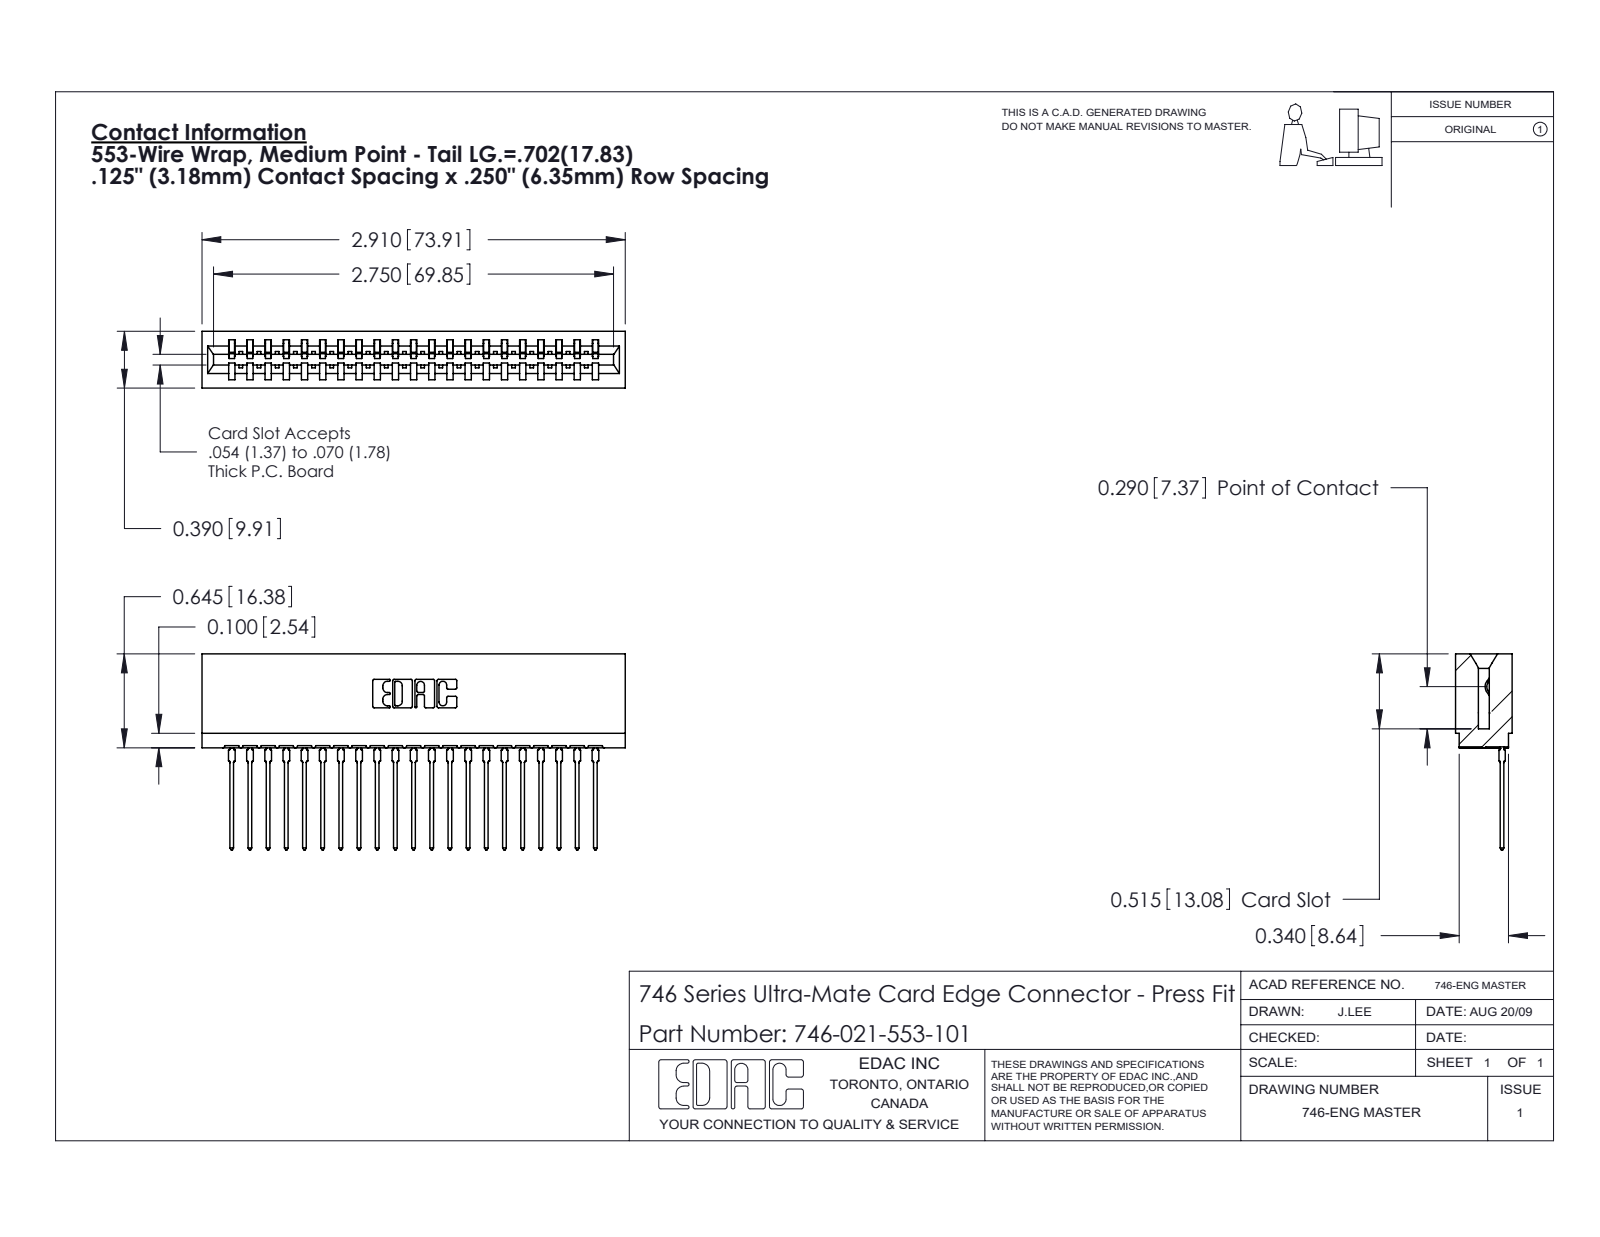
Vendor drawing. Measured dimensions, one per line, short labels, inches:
name: 746 Part_.515 Slot Depth - 01; 746-021-553-101; 746-292-001_553
written by: SolidWorks 2020 (CONFIG_CONTROL_DESIGN)
unit: in
bodies: 22 solids, 2365 faces (1378 planar, 441 cylindrical, 546 other)
size: 2.91 × 1.346 × 0.39
volume: 0.485 in³; area: 18.32 in²
rounds: 42× R0.021, 22× R0.01, 22× R0.015, 6× R0.007, 6× R0.031, 4× R0.005, 4× R0.011, 3× R0.026
face distances: 0.25, 0.333, 0.057, 0.39, 0.5, 0.025, 0.307, 0.083, 0.042, 0.125
